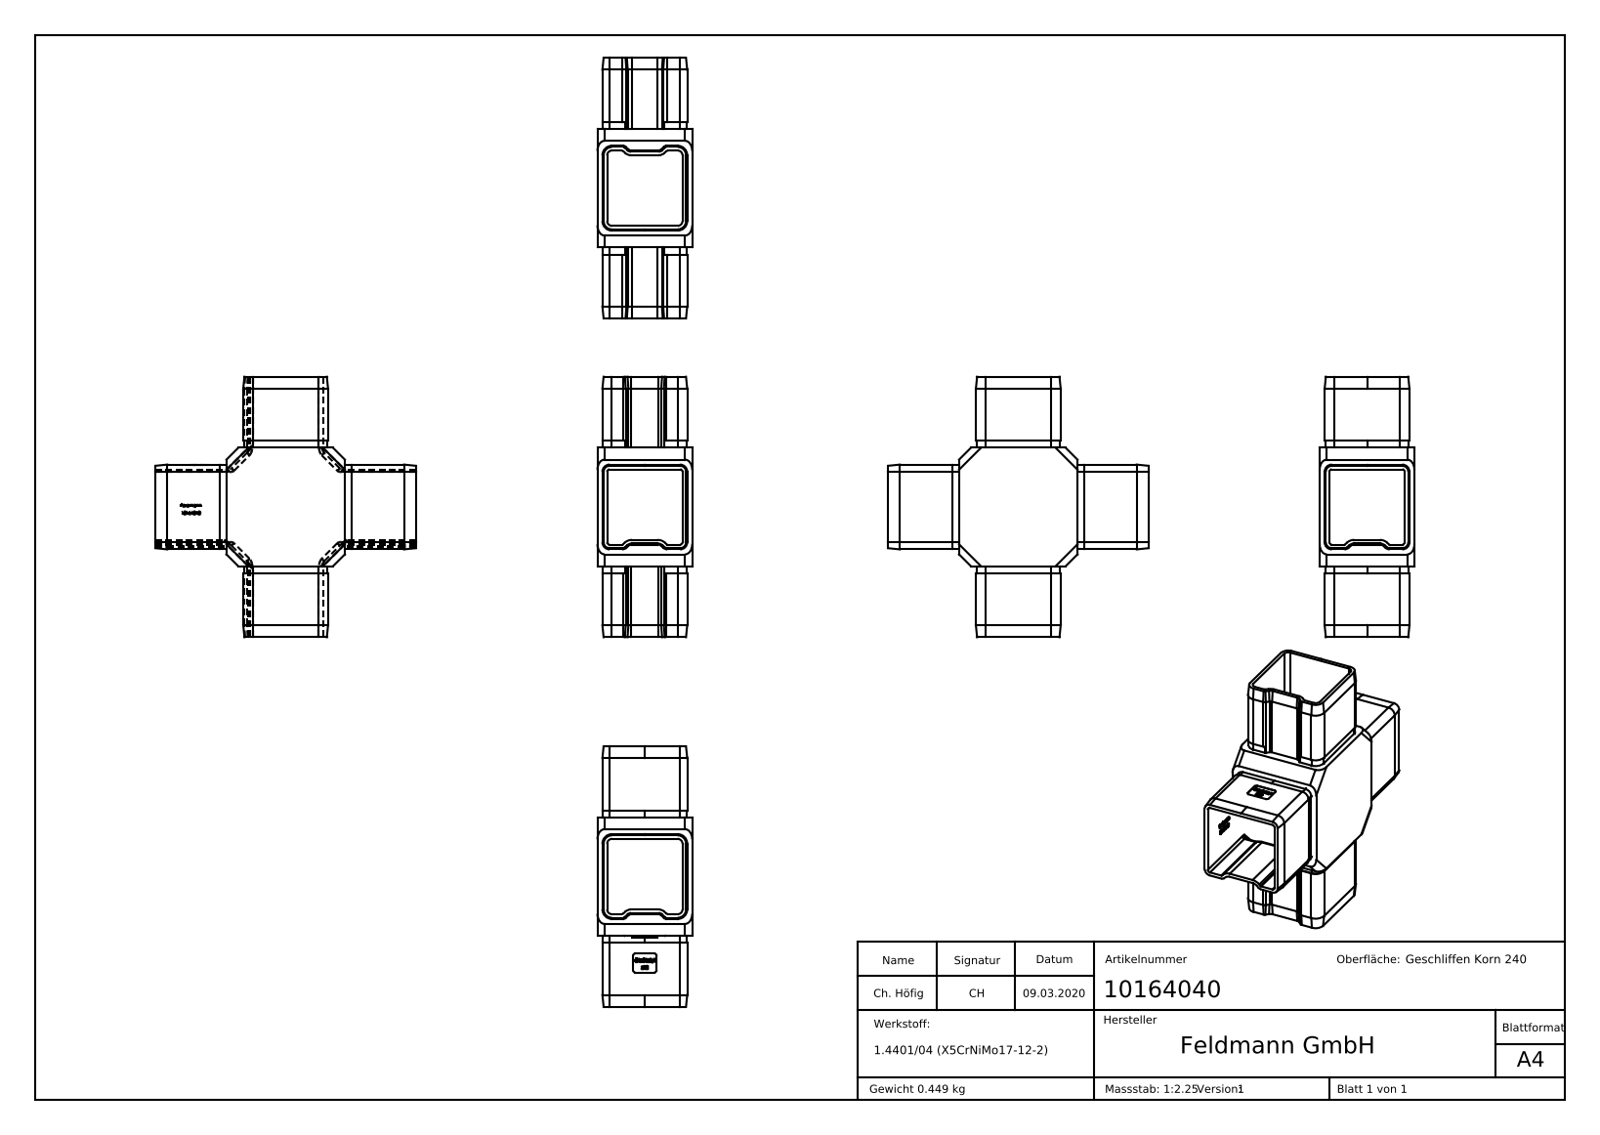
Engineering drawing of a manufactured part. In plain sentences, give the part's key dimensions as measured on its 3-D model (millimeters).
The part is named "10164040". Its 3-D file was written by "SolidWorks 2015 (CONFIG_CONTROL_DESIGN)". It is 1 solid with 739 faces: 402 planar, 124 cylindrical and 213 other. Overall it measures 110 by 110 by 40 millimeters. Its volume is 56 172 cubic millimeters and its surface area 46 424 square millimeters. Partial cylindrical surfaces (rounded edges, fillets, slot ends): 34 of radius 1.5, 12 of radius 3, 8 of radius 1, 4 of radius 2, 4 of radius 2.46, 4 of radius 2.7, 4 of radius 3.7, 4 of radius 4. The main face-to-face distances are 2, 31.8, 33.8, 4.1, 2.1, 35.9, 37.9, 35.8, 40, 7.1.
